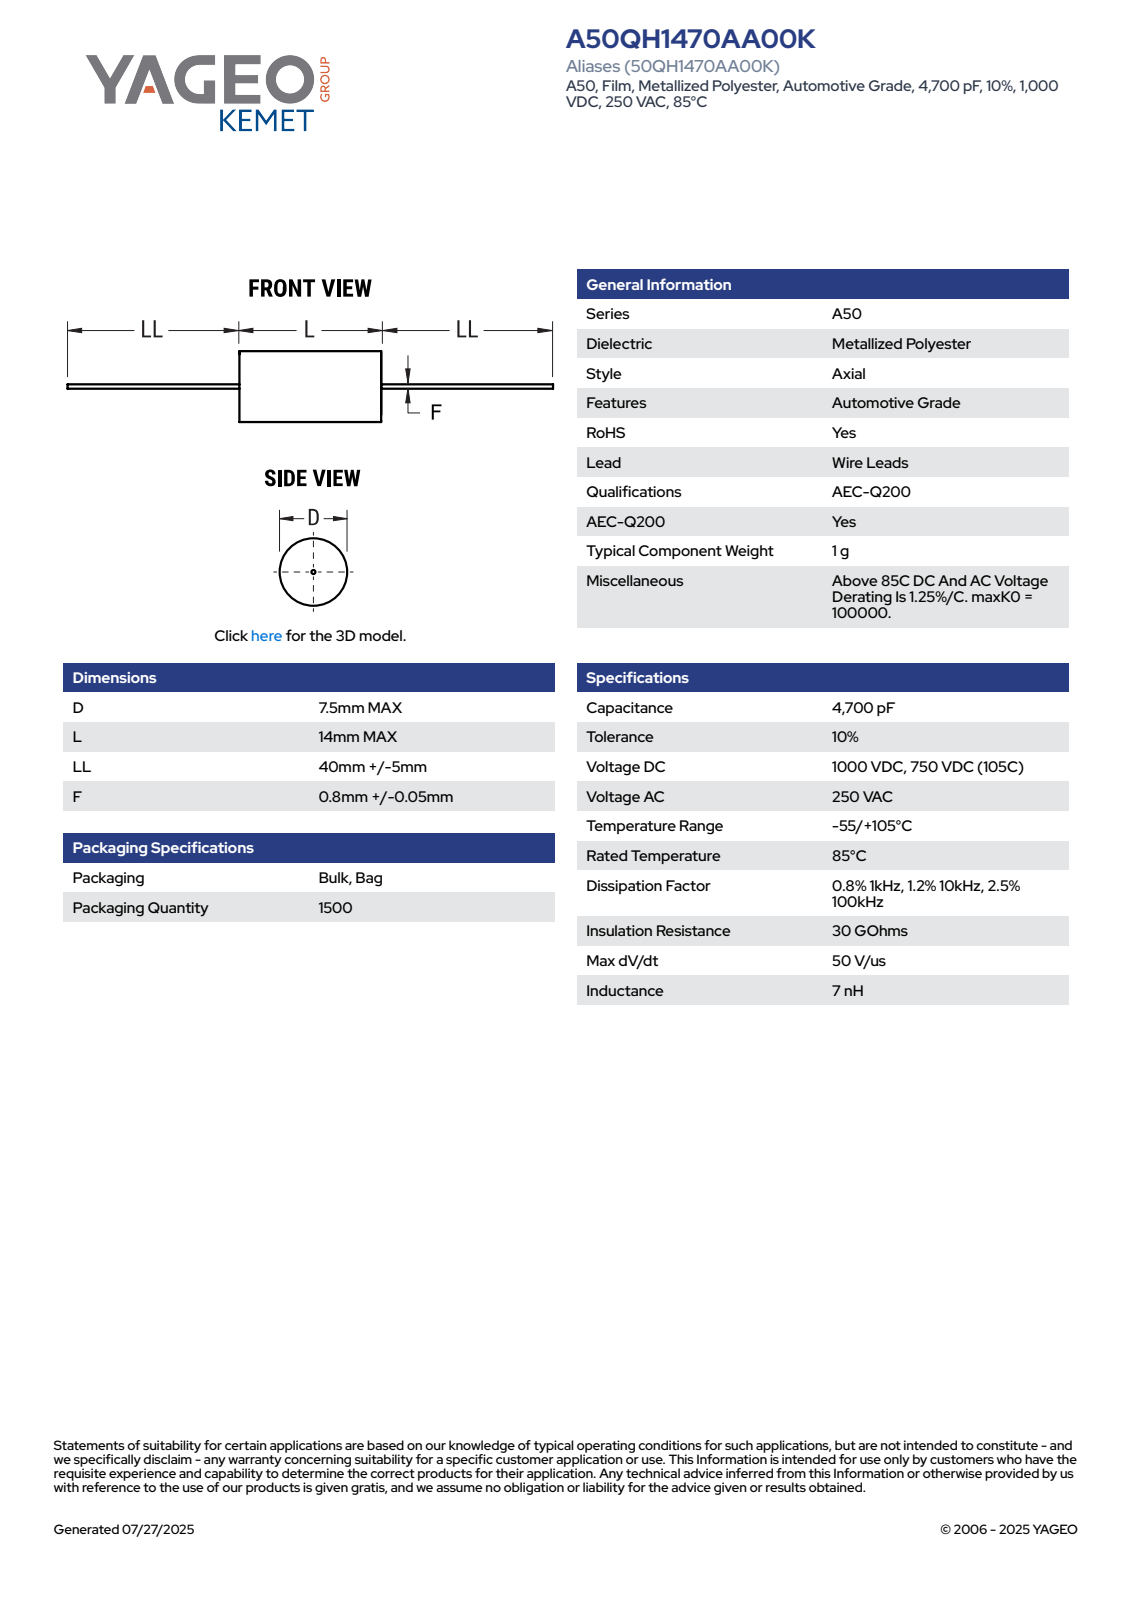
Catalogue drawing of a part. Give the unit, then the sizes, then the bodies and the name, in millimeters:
Units: millimetres
Overall size (bounding box): 104 × 7.51 × 7.5
Round bosses / shafts (diameter × count): ⌀7.5 ×1, ⌀0.85 ×1
Partial cylindrical surfaces — rounded edges, fillets, slot ends (radius × count): R3.76 ×1
Main face-to-face distances: 14, 45, 59, 104
Volume: 670 mm³ · Surface area: 659 mm²
Bodies: 1 solid, 72 faces (26 planar, 15 cylindrical, 31 other)
Part name (STEP PRODUCT): CFA_ACWF_7.5X14_D7.5L14LL45F0.85
STEP written by: SolidWorks 2014 (AUTOMOTIVE_DESIGN)
